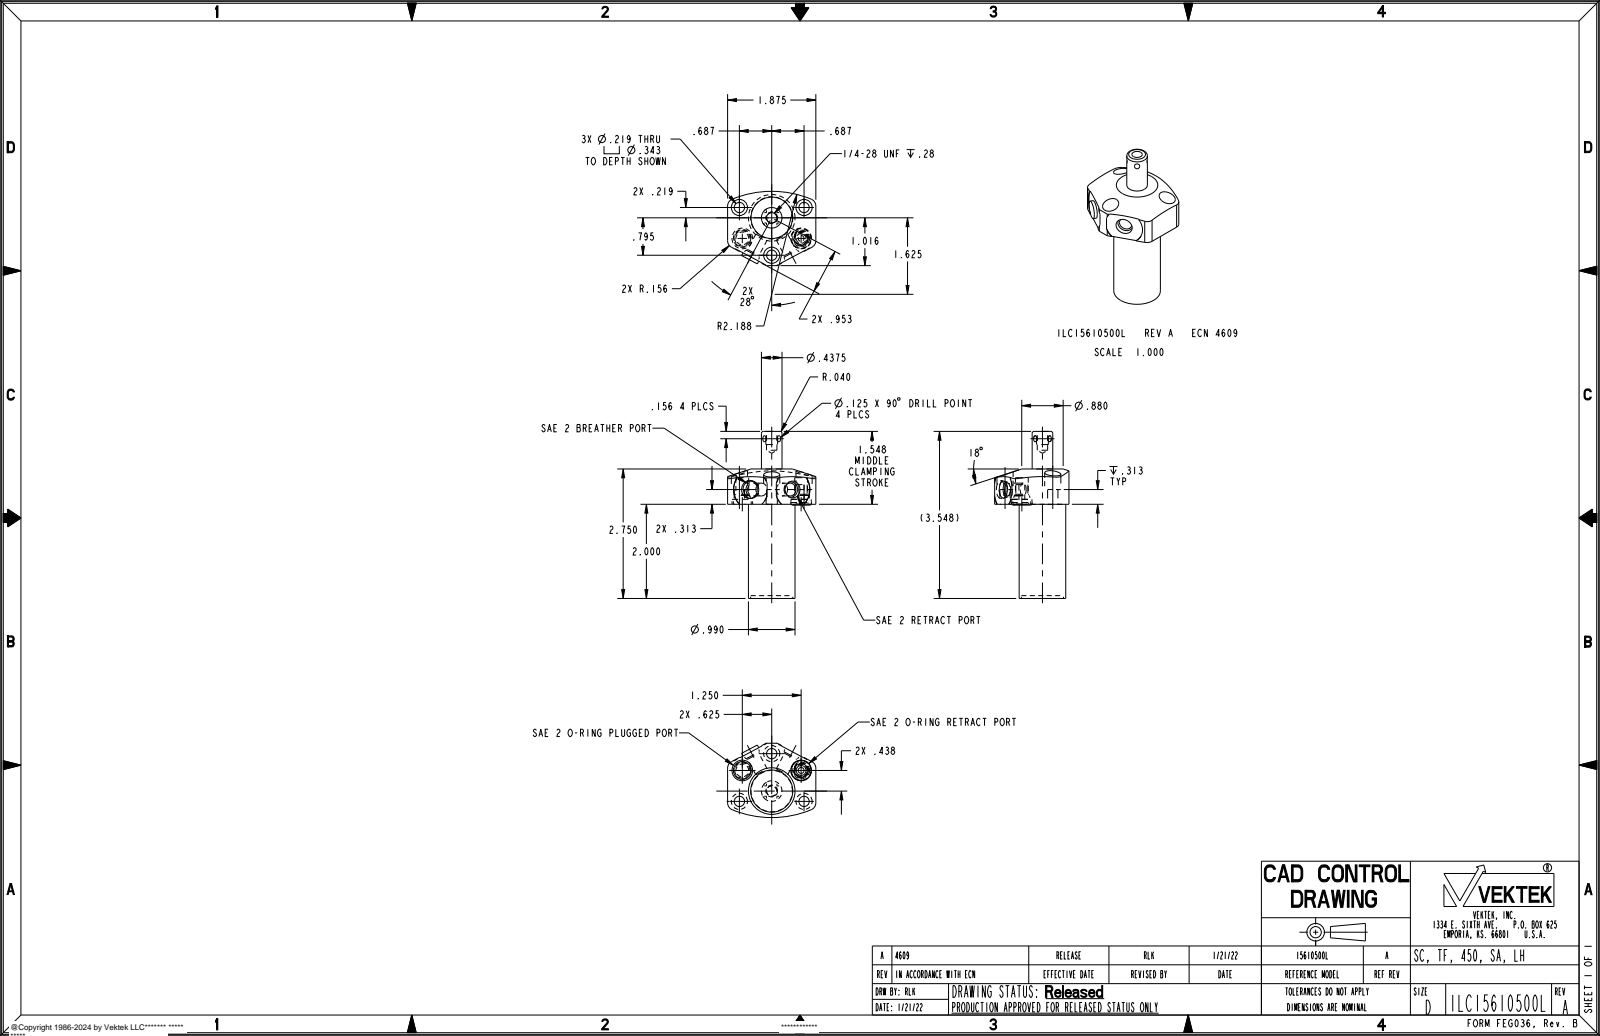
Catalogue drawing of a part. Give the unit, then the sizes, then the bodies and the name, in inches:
Units: inches
Overall size (bounding box): 3.548 × 2.075 × 1.779
Round holes (diameter × count): ⌀0.272 ×4, ⌀0.219 ×3, ⌀0.343 ×3, ⌀0.438 ×2, ⌀0.125 ×1, ⌀0.221 ×1, ⌀0.895 ×1
Round bosses / shafts (diameter × count): ⌀0.378 ×2, ⌀0.99 ×1, ⌀0.437 ×1, ⌀0.43 ×1, ⌀0.256 ×1, ⌀0.25 ×1, ⌀0.21 ×1
Partial cylindrical surfaces — rounded edges, fillets, slot ends (radius × count): R0.156 ×4, R0.412 ×2, R2.188 ×1
Main face-to-face distances: 1.94, 2.69, 0.75, 1.875, 0.105, 0.313, 2.045, 0.645, 2.253, 0.208
Hole centre spacings: 0.66, 0.72, 0.721, 0.763, 1.225, 1.468, 0.795, 1.25
Volume: 3.039 in³ · Surface area: 21.26 in²
Bodies: 1 solid, 126 faces (35 planar, 57 cylindrical, 34 other)
Part name (STEP PRODUCT): ILC15610500L
STEP written by: CREO PARAMETRIC BY PTC INC, 2021164 (AUTOMOTIVE_DESIGN)
